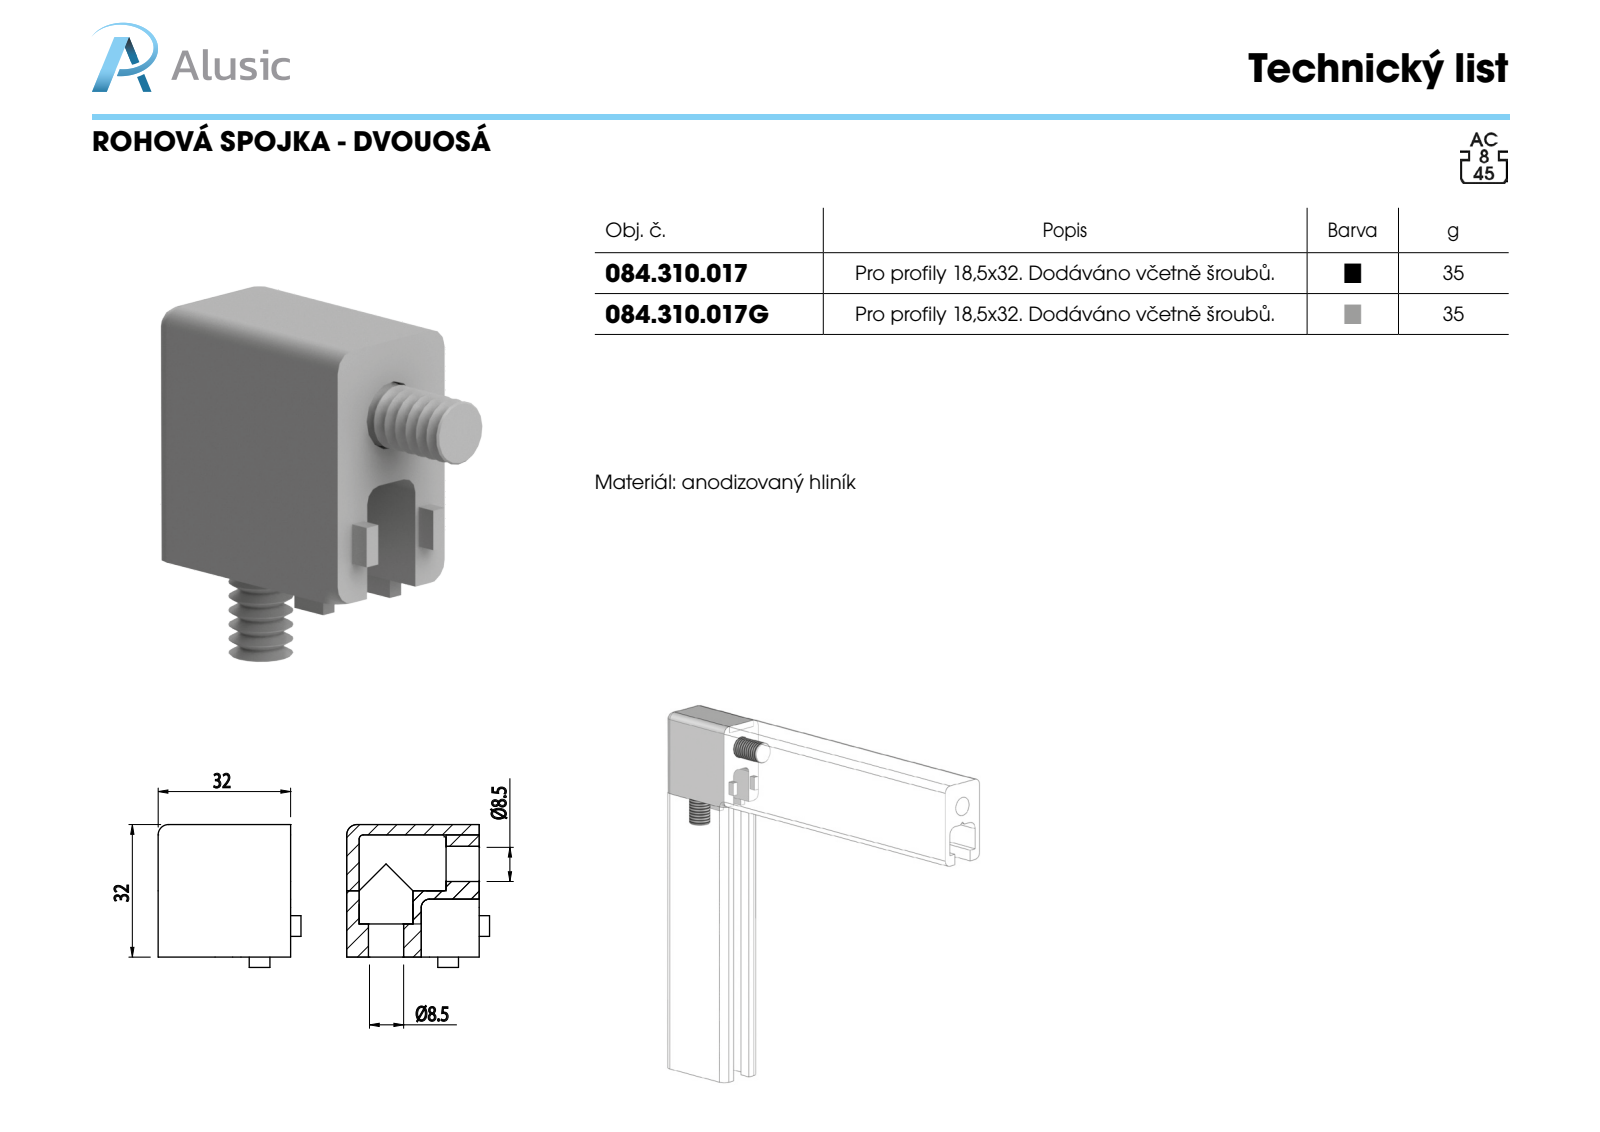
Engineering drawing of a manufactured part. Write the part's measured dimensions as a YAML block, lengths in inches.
part_name: "084.301.000 VITI ALUSIC_084.301.003; 084.310.017-2; 084.310.017; 084.310.017-1"
step_written_by: "SolidWorks 2011 (CONFIG_CONTROL_DESIGN)"
units: inches
bodies: {solids: 4, faces: 134, planar: 71, cylindrical: 48, other: 15}
overall_size: [1.732, 1.732, 0.728]
volume: 0.907
surface_area: 15.03
round_holes:
  - {diameter: 0.079, count: 2}
  - {diameter: 0.098, count: 2}
  - {diameter: 0.335, count: 2}
  - {diameter: 0.512, count: 1}
round_bosses_or_shafts:
  - {diameter: 0.315, count: 2}
  - {diameter: 0.512, count: 1}
partial_cylinders:
  - {radius: 0.079, count: 5}
  - {radius: 0.098, count: 5}
  - {radius: 0.02, count: 2}
  - {radius: 0.039, count: 1}
face_to_face_distances: [0.728, 1.26, 0.108, 0.62, 0.512, 0.098, 0.315, 0.945, 1.161, 0.201]
hole_center_spacings: [0.343, 0.754, 1.034, 1.093, 0.315, 0.394]
